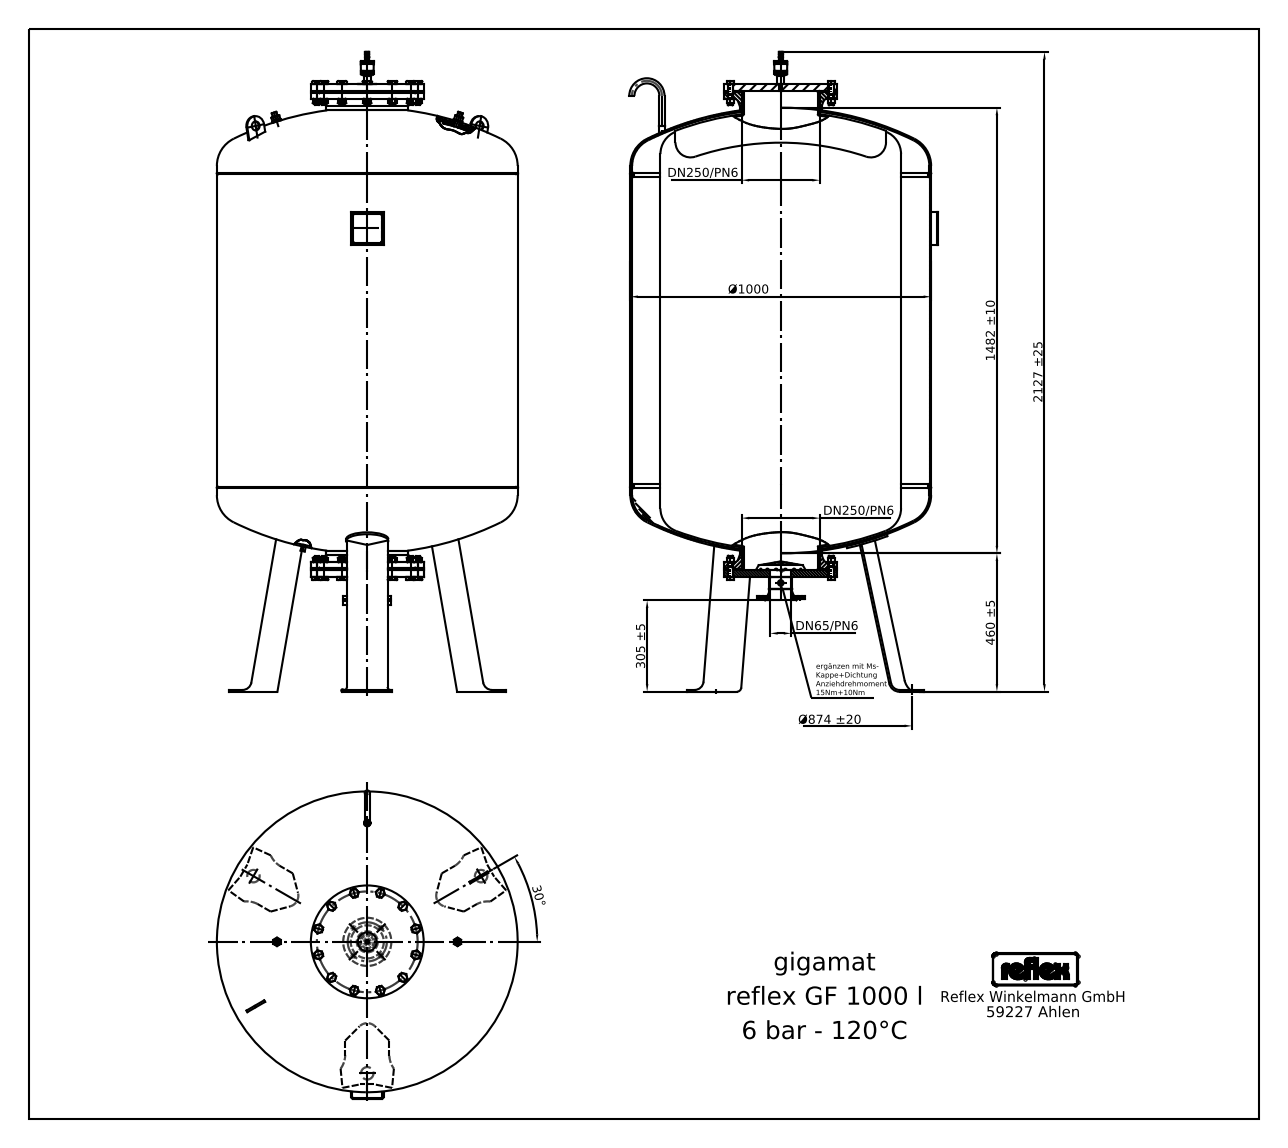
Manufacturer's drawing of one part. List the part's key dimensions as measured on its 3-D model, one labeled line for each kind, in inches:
STEP written by: Mechanical Desktop 2008 (CONFIG_CONTROL_DESIGN)
Units: inches
Bodies: 20 solids, 863 faces (529 planar, 214 cylindrical, 120 other)
Overall size (bounding box): 83.74 × 39.37 × 39.37
Volume: 65 170 in³ · Surface area: 16 320 in²
Round holes (diameter × count): ⌀1.181 ×1, ⌀10.252 ×1
Round bosses / shafts (diameter × count): ⌀0.63 ×12, ⌀0.654 ×2, ⌀0.472 ×2, ⌀39.37 ×1, ⌀14.764 ×1, ⌀10.748 ×1, ⌀10.724 ×1, ⌀2.996 ×1
Partial cylindrical surfaces — rounded edges, fillets, slot ends (radius × count): R0.984 ×18, R0.332 ×4, R0.133 ×3, R0.354 ×3, R0.227 ×2, R0.398 ×2, R0.548 ×2, R0.555 ×2
Main face-to-face distances: 41.142, 0.866, 63.583, 1.063, 62.52, 51.988, 10.846, 52.854, 11.713, 11.594
